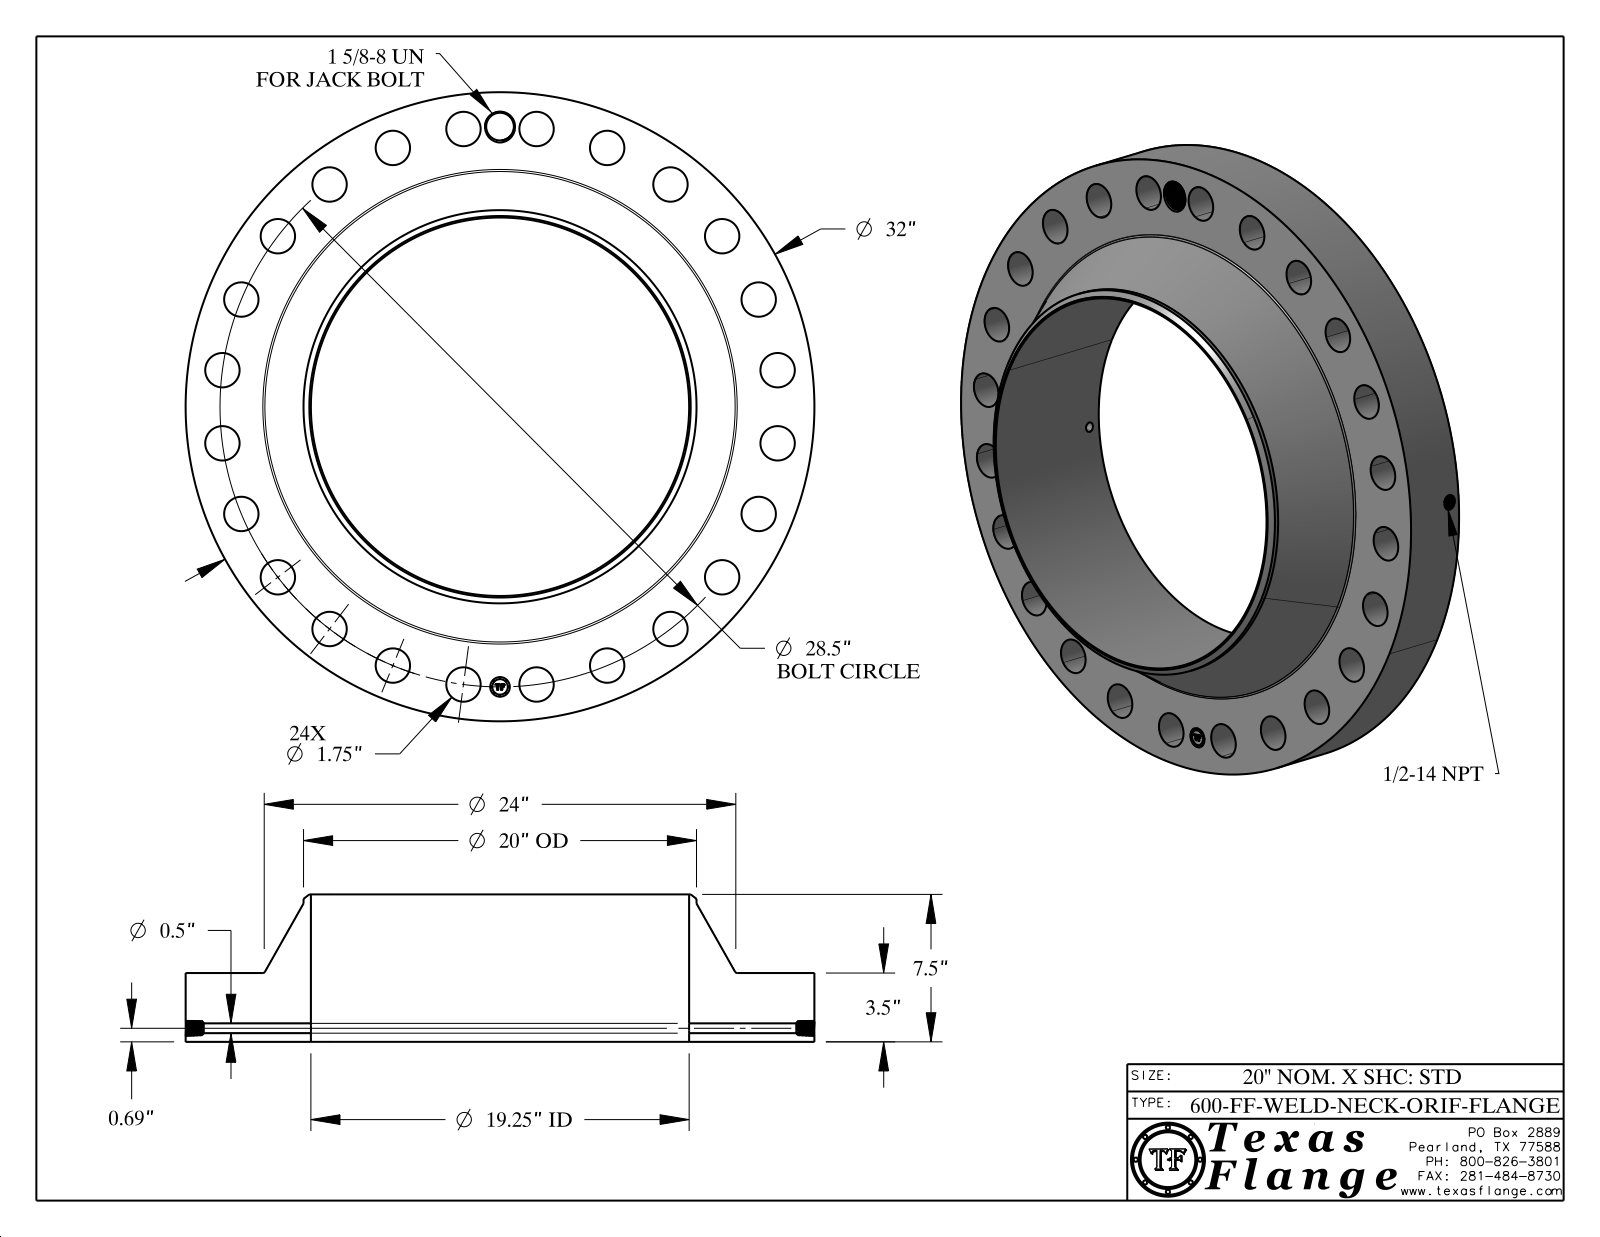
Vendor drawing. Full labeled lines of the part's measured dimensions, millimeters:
Part name (STEP PRODUCT): 600-FF-WELD-NECK
STEP written by: CATIA V5 STEP AP214 (AUTOMOTIVE_DESIGN)
Units: millimetres
Bodies: 1 solid, 876 faces (368 planar, 149 cylindrical, 359 other)
Overall size (bounding box): 812.8 × 812.8 × 190.5
Volume: 31 330 000 mm³ · Surface area: 1 544 000 mm²
Round holes (diameter × count): ⌀44.5 ×24, ⌀12.7 ×1, ⌀17.1 ×1, ⌀25.4 ×1, ⌀35.8 ×1, ⌀489 ×1
Round bosses / shafts (diameter × count): ⌀1.5 ×8, ⌀812.8 ×1, ⌀508 ×1, ⌀20 ×1
Main face-to-face distances: 88.9, 190.5, 101.6, 88.5, 0.4, 102, 7.6, 7.4, 1.4, 6.3
Hole centre spacings: 362, 440.7, 626.9, 717.7, 277, 94.5, 187.4, 511.9
